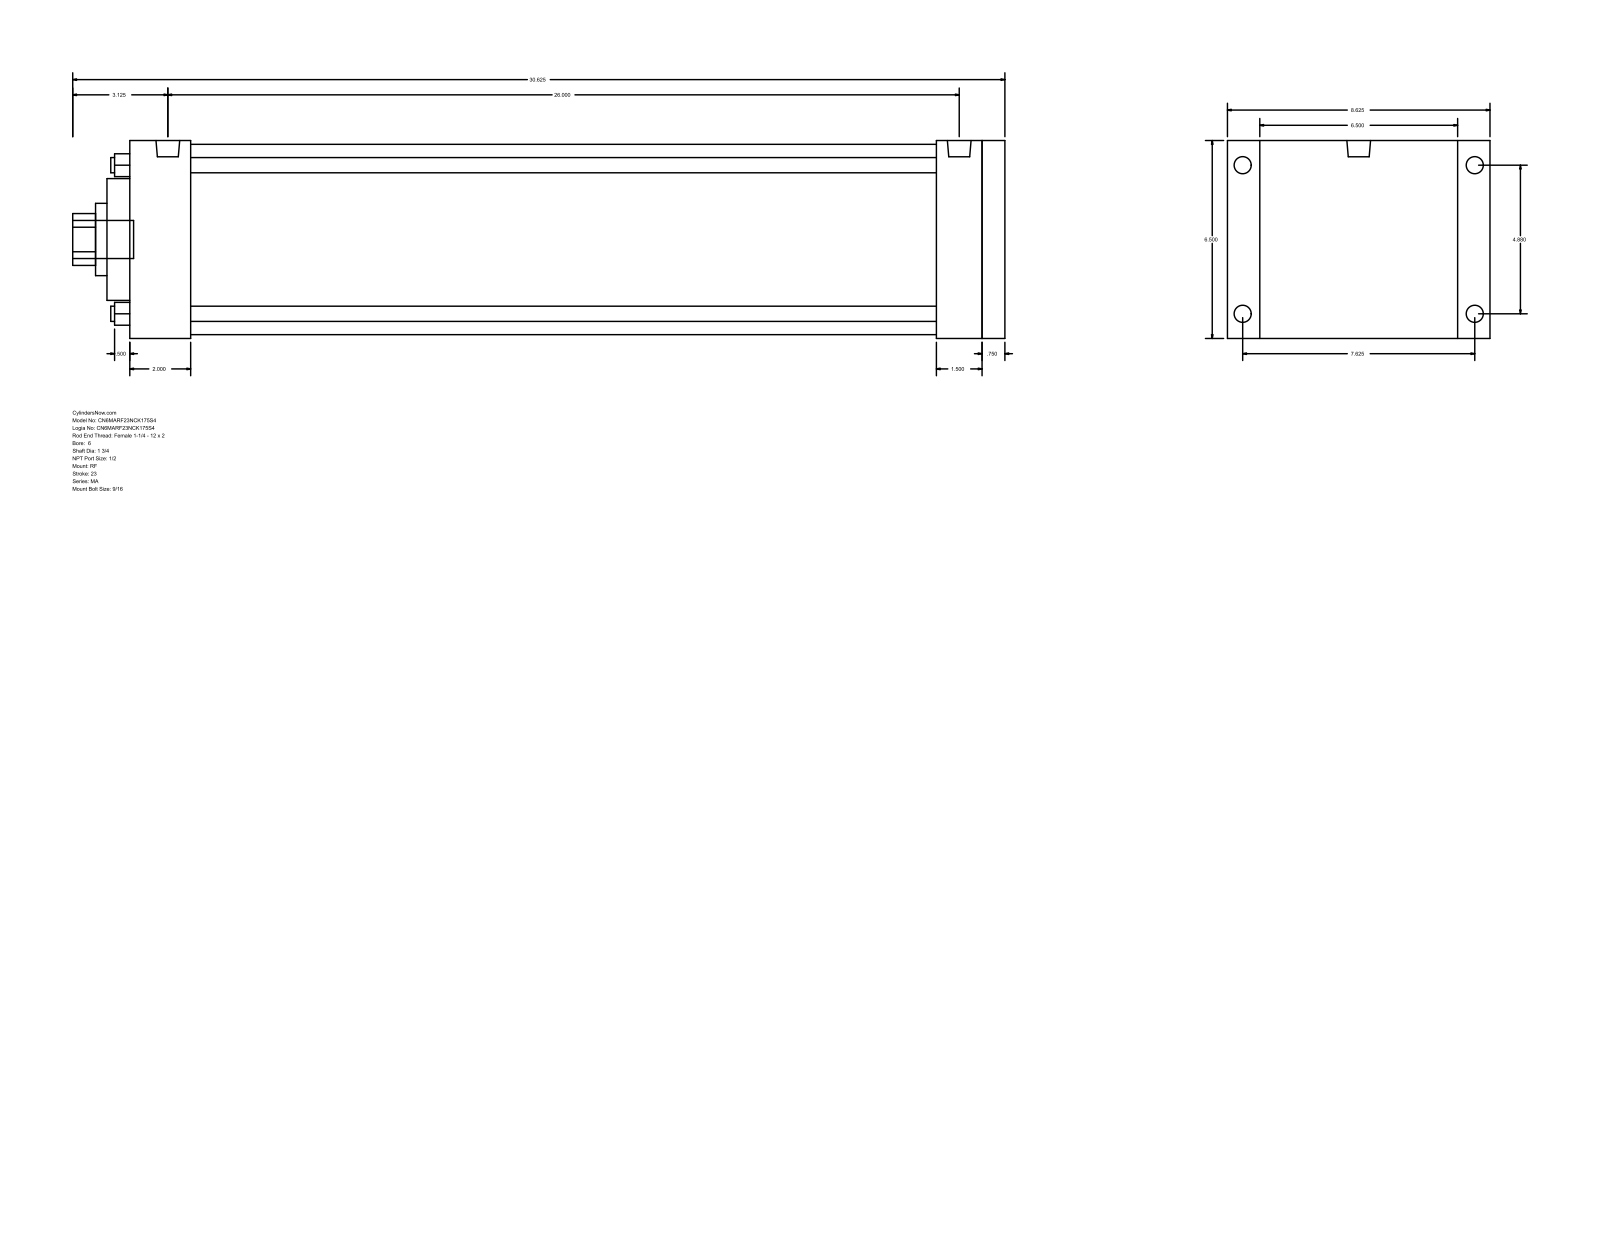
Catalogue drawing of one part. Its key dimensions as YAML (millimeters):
part_name: "MA_RF__0600_1.75"
step_written_by: "GSSL Pune (CONFIG_CONTROL_DESIGN)"
units: millimeters
bodies: {solids: 0, faces: 94, planar: 65, cylindrical: 29, other: 0}
overall_size: [777.88, 219.07, 165.1]
round_holes:
  - {diameter: 12.7, count: 4}
  - {diameter: 44.45, count: 1}
  - {diameter: 60.33, count: 1}
  - {diameter: 101.6, count: 1}
  - {diameter: 158.75, count: 1}
round_bosses_or_shafts:
  - {diameter: 17.46, count: 4}
  - {diameter: 14.29, count: 4}
  - {diameter: 19.77, count: 2}
  - {diameter: 31.75, count: 1}
partial_cylinders:
  - {radius: 21.63, count: 1}
face_to_face_distances: [165.1, 730.26, 19.05, 711.21, 38.1, 50.8, 660.41, 679.46, 673.11, 622.31]
hole_center_spacings: [87.65, 123.96, 175.31]
